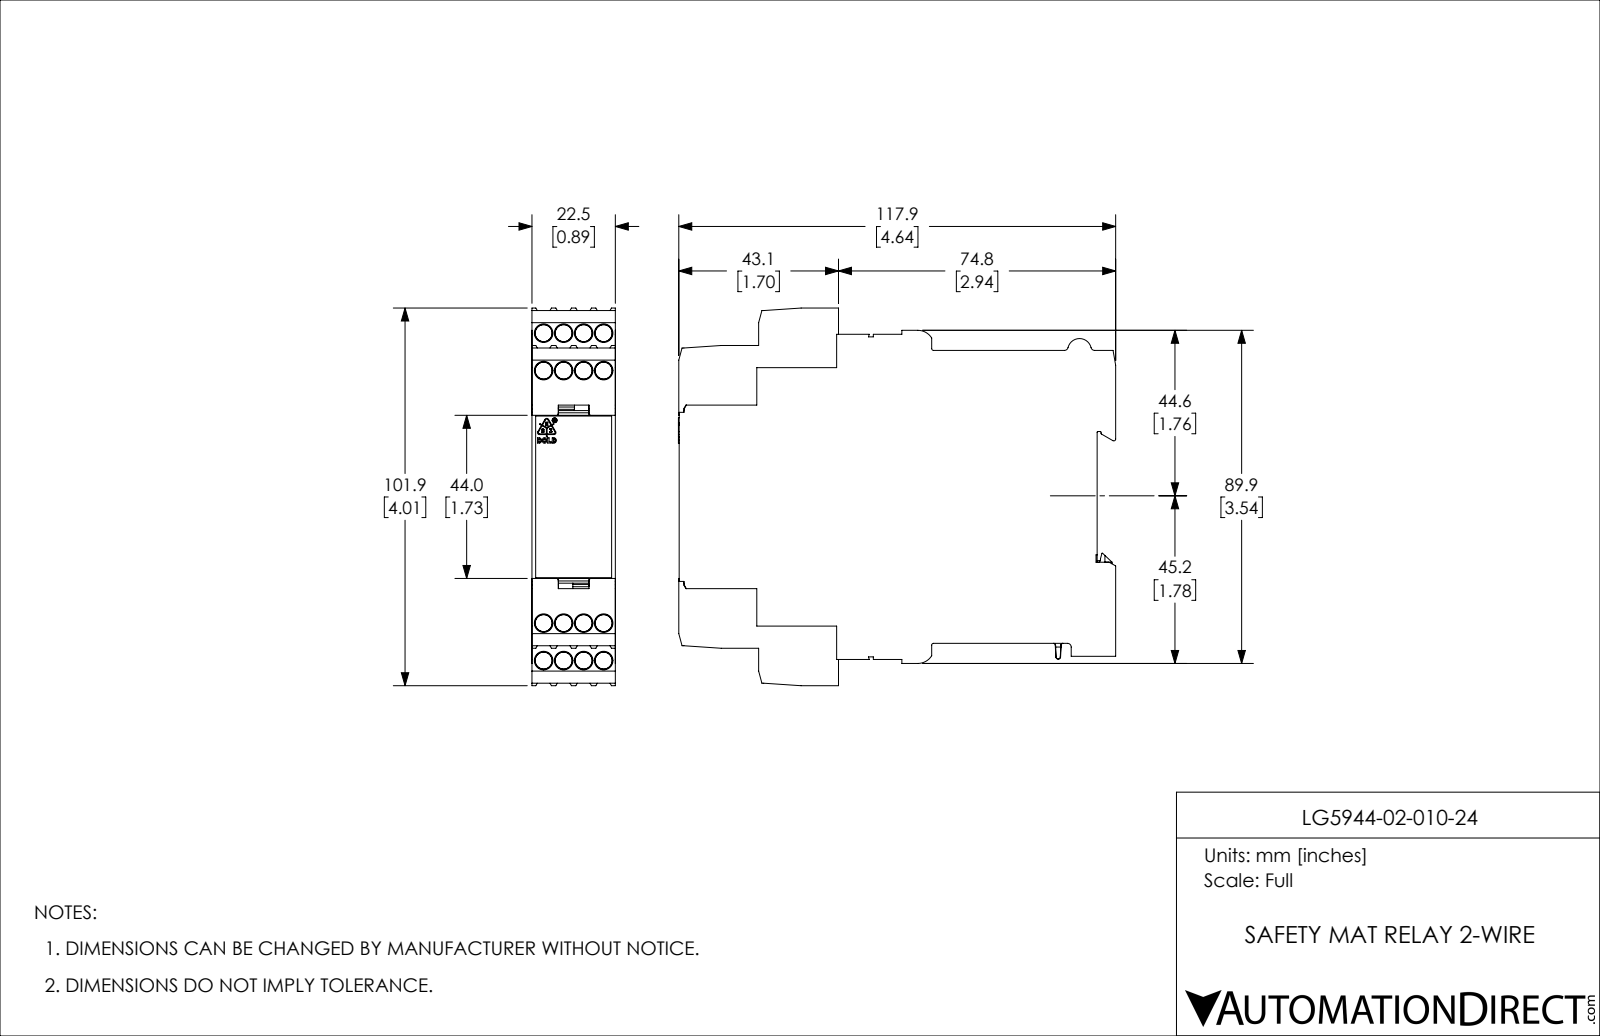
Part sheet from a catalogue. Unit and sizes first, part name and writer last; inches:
Units: inches
Overall size (bounding box): 4.646 × 4.01 × 0.886
Round holes (diameter × count): ⌀0.039 ×4, ⌀0.067 ×4, ⌀0.049 ×1
Round bosses / shafts (diameter × count): ⌀0.053 ×1
Partial cylindrical surfaces — rounded edges, fillets, slot ends (radius × count): R0.004 ×10, R0.02 ×7, R0.005 ×6, R0.039 ×6, R0.004 ×4, R0.008 ×3, R0.021 ×3, R0.012 ×2
Main face-to-face distances: 0.886, 0.171, 3.11, 4.439, 3.281, 0.197, 4.636, 0.398, 4.642, 4.445
Hole centre spacings: 0.638, 0.848, 1.061
Volume: 13.57 in³ · Surface area: 49.38 in²
Bodies: 1 solid, 778 faces (665 planar, 79 cylindrical, 34 other)
Part name (STEP PRODUCT): LG5944-02-010-24
STEP written by: SolidWorks 2018 (AUTOMOTIVE_DESIGN)
